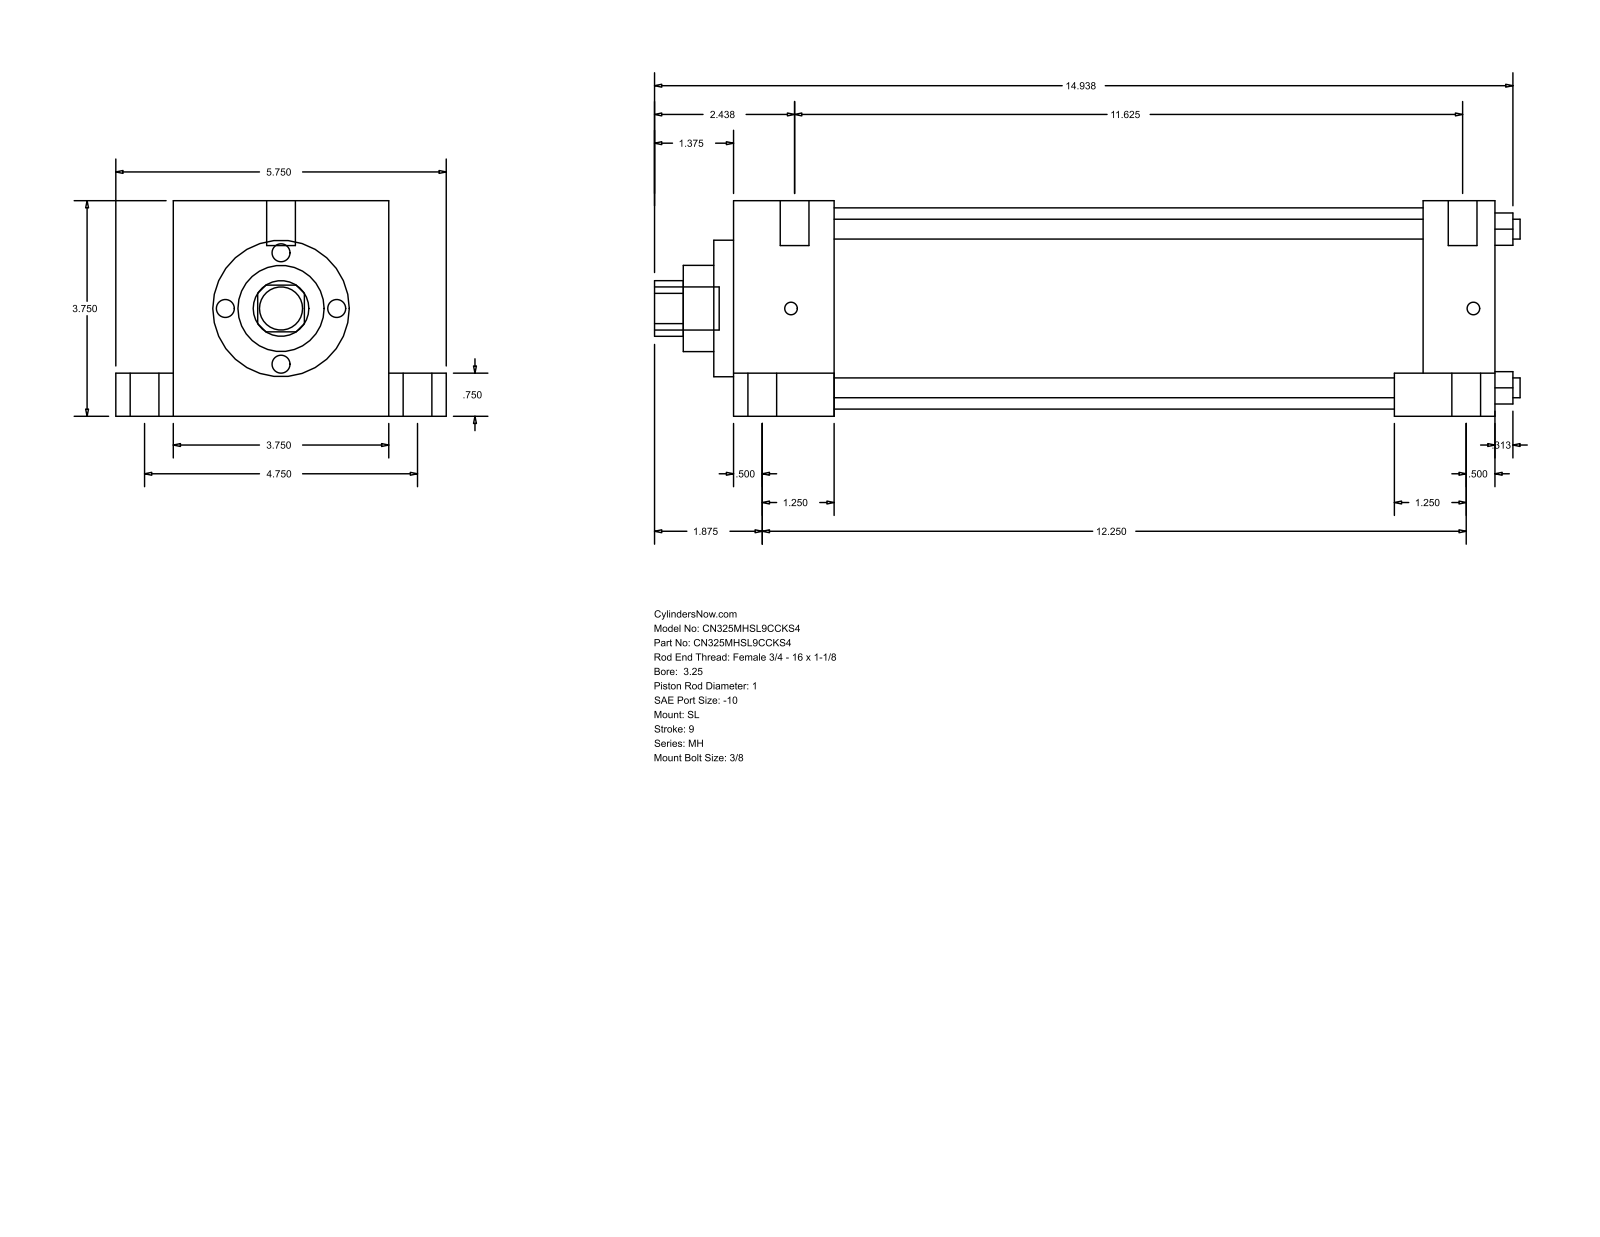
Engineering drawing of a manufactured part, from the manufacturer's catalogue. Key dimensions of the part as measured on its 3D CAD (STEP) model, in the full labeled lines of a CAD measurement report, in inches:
Part name (STEP PRODUCT): MH_SL__0325_1
STEP written by: GSSL Pune (CONFIG_CONTROL_DESIGN)
Units: inches
Bodies: 0 solids, 110 faces (77 planar, 33 cylindrical, 0 other)
Overall size (bounding box): 15.063 × 5.75 × 3.75
Round holes (diameter × count): ⌀0.345 ×4, ⌀1 ×1, ⌀1.5 ×1, ⌀2.375 ×1, ⌀3.5 ×1
Round bosses / shafts (diameter × count): ⌀0.5 ×6, ⌀0.75 ×5, ⌀0.219 ×4
Partial cylindrical surfaces — rounded edges, fillets, slot ends (radius × count): R0.484 ×1
Main face-to-face distances: 3.75, 13.25, 1.75, 11.5, 1, 4.75, 0.75, 3, 12, 10.25
Hole centre spacings: 1.952, 2.76, 3.903
